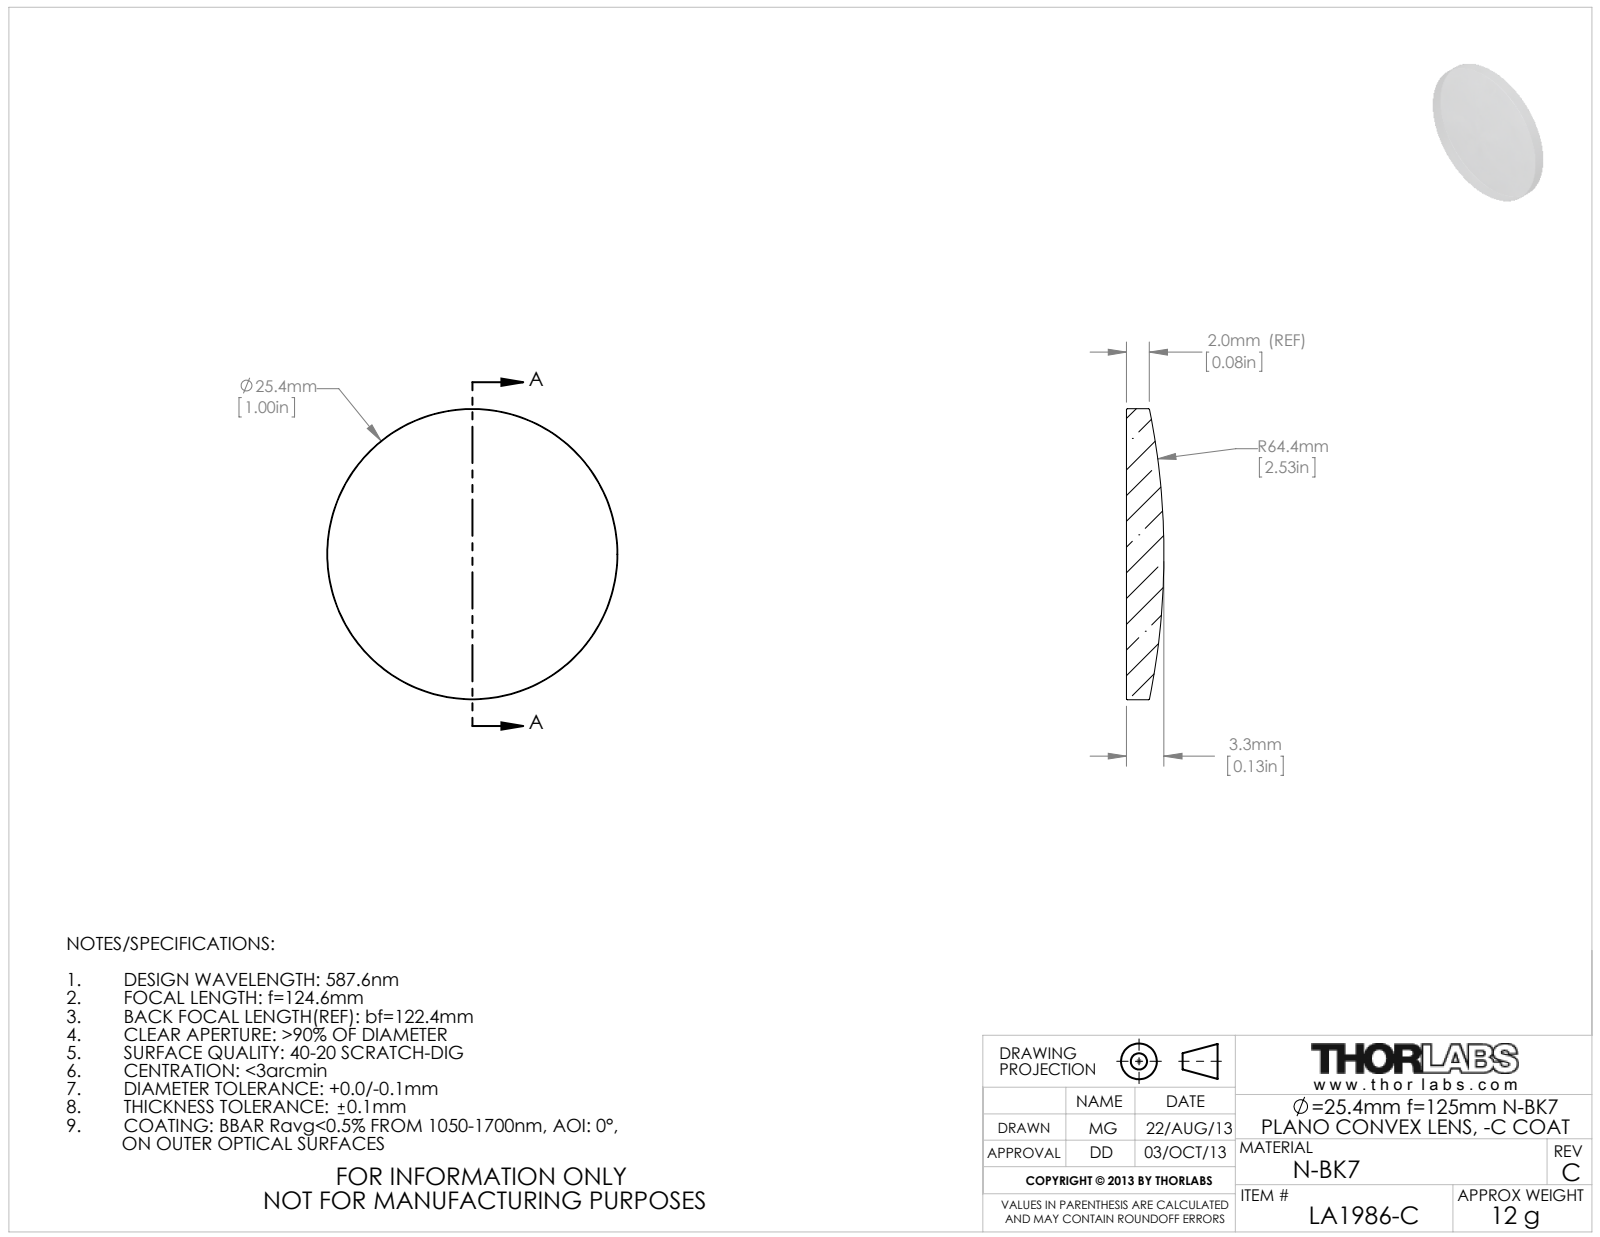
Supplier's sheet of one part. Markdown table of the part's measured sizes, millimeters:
| quantity | value |
| --- | --- |
| part name | 4585-E0W |
| STEP written by | SolidWorks 2009 (AUTOMOTIVE_DESIGN) |
| units | millimeters |
| bodies | 1 solid, 5 faces (1 planar, 2 cylindrical, 2 other) |
| overall size | 25.4 × 25.4 × 3.26 |
| volume | 1 332 mm³ |
| surface area | 1 178 mm² |
| round bosses / shafts (diameter × count) | 25.4 × 1 |
